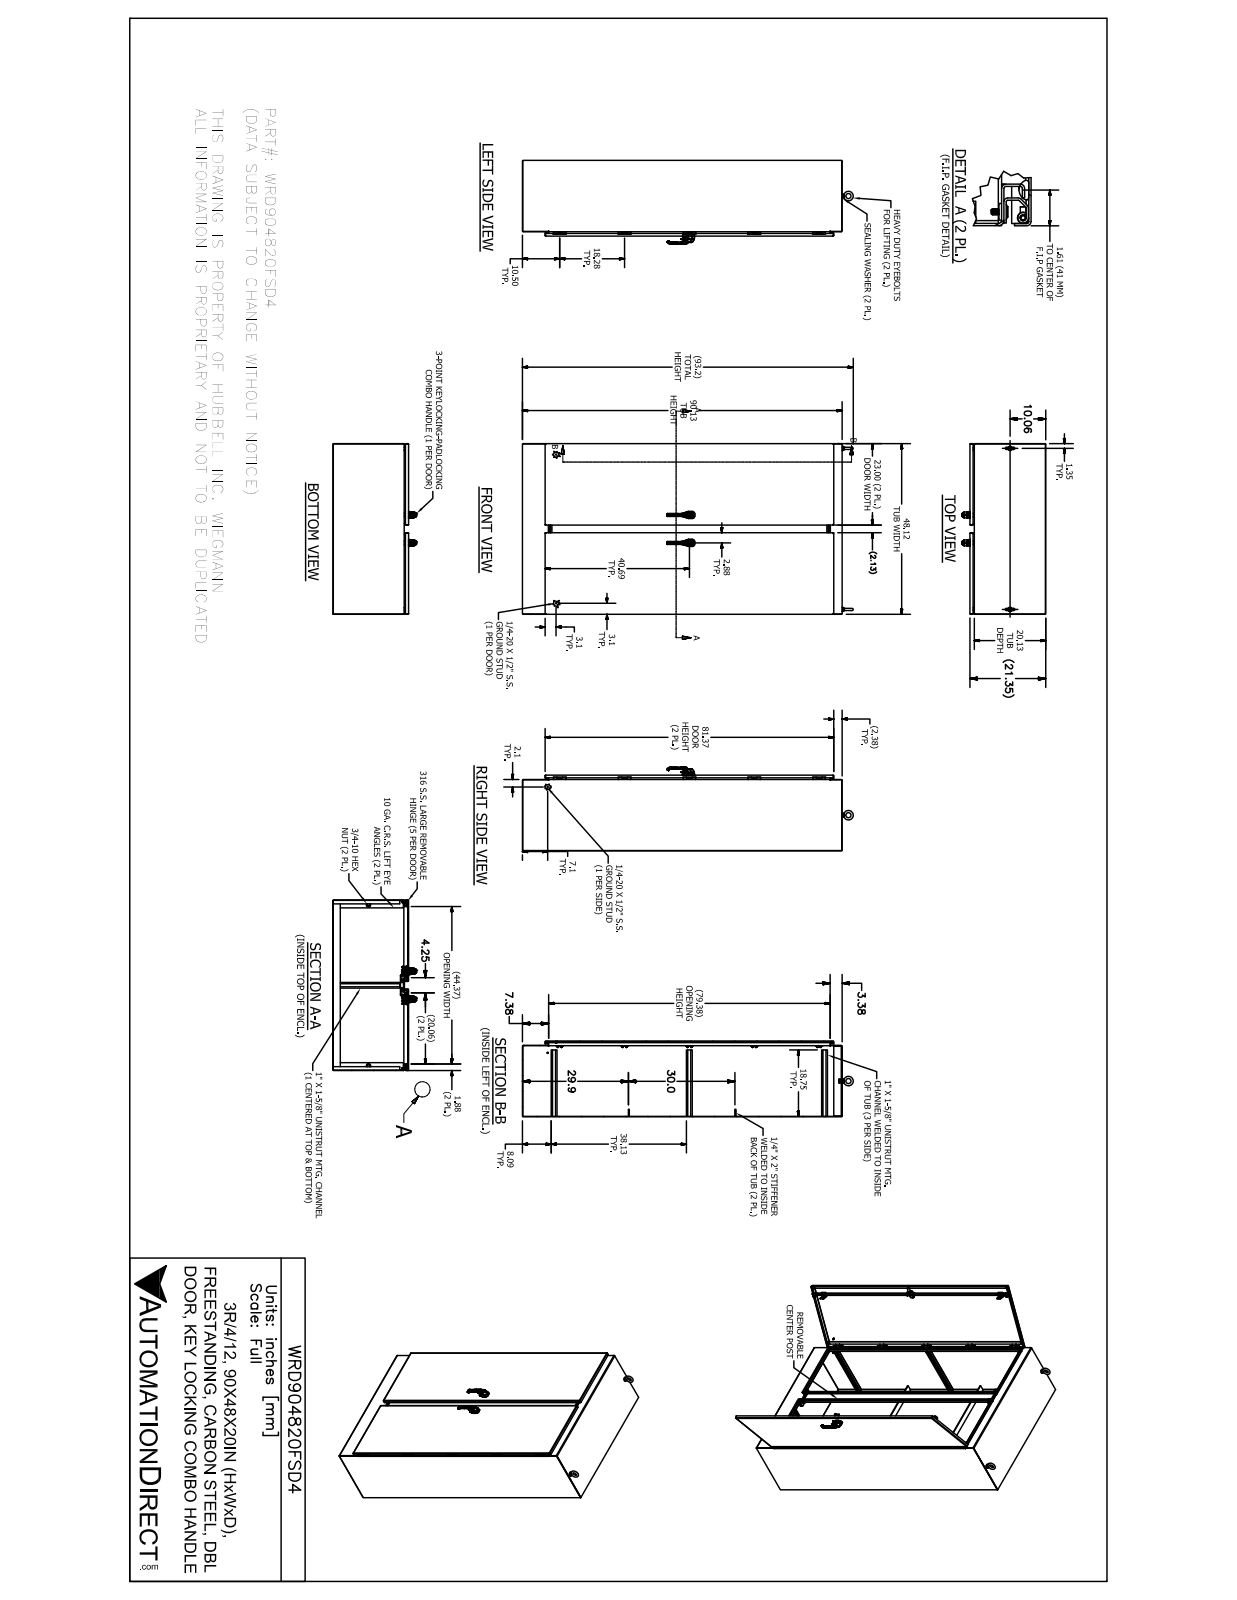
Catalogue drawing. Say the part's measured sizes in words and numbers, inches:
The part is named "WRD904820FSD4". Its 3-D file was written by "SolidWorks 2017 (AUTOMOTIVE_DESIGN)". It is 170 solids with 3566 faces: 1654 planar, 1190 cylindrical and 722 other. Overall it measures 93.248 by 48.133 by 23.527 inches. Its volume is 1 969 cubic inches and its surface area 35 831 square inches. Round holes: 24 of diameter 0.266, 20 of diameter 0.23, 20 of diameter 0.281, 20 of diameter 0.65, 8 of diameter 0.2, 8 of diameter 0.277, 6 of diameter 0.281, 4 of diameter 0.156, 4 of diameter 0.252, 4 of diameter 0.4, 4 of diameter 0.45, 3 of diameter 0.241. Round bosses or shafts: 17 of diameter 0.625, 14 of diameter 0.25, 4 of diameter 0.533, 4 of diameter 0.438, 4 of diameter 0.375, 4 of diameter 0.313, 4 of diameter 0.213, 3 of diameter 1. Partial cylindrical surfaces (rounded edges, fillets, slot ends): 44 of radius 0.062, 36 of radius 0.125, 32 of radius 0.05, 28 of radius 0.063, 20 of radius 0.01, 16 of radius 0.019, 16 of radius 0.025, 16 of radius 0.053. The main face-to-face distances are 0.104, 21.245, 21.141, 21.349, 48.021, 90.021, 47.917, 48.125, 20.021, 1.224. The hole center spacings are 18.281, 50.314, 1, 46.875, 46.886, 36.563, 50.686, 59.448.
